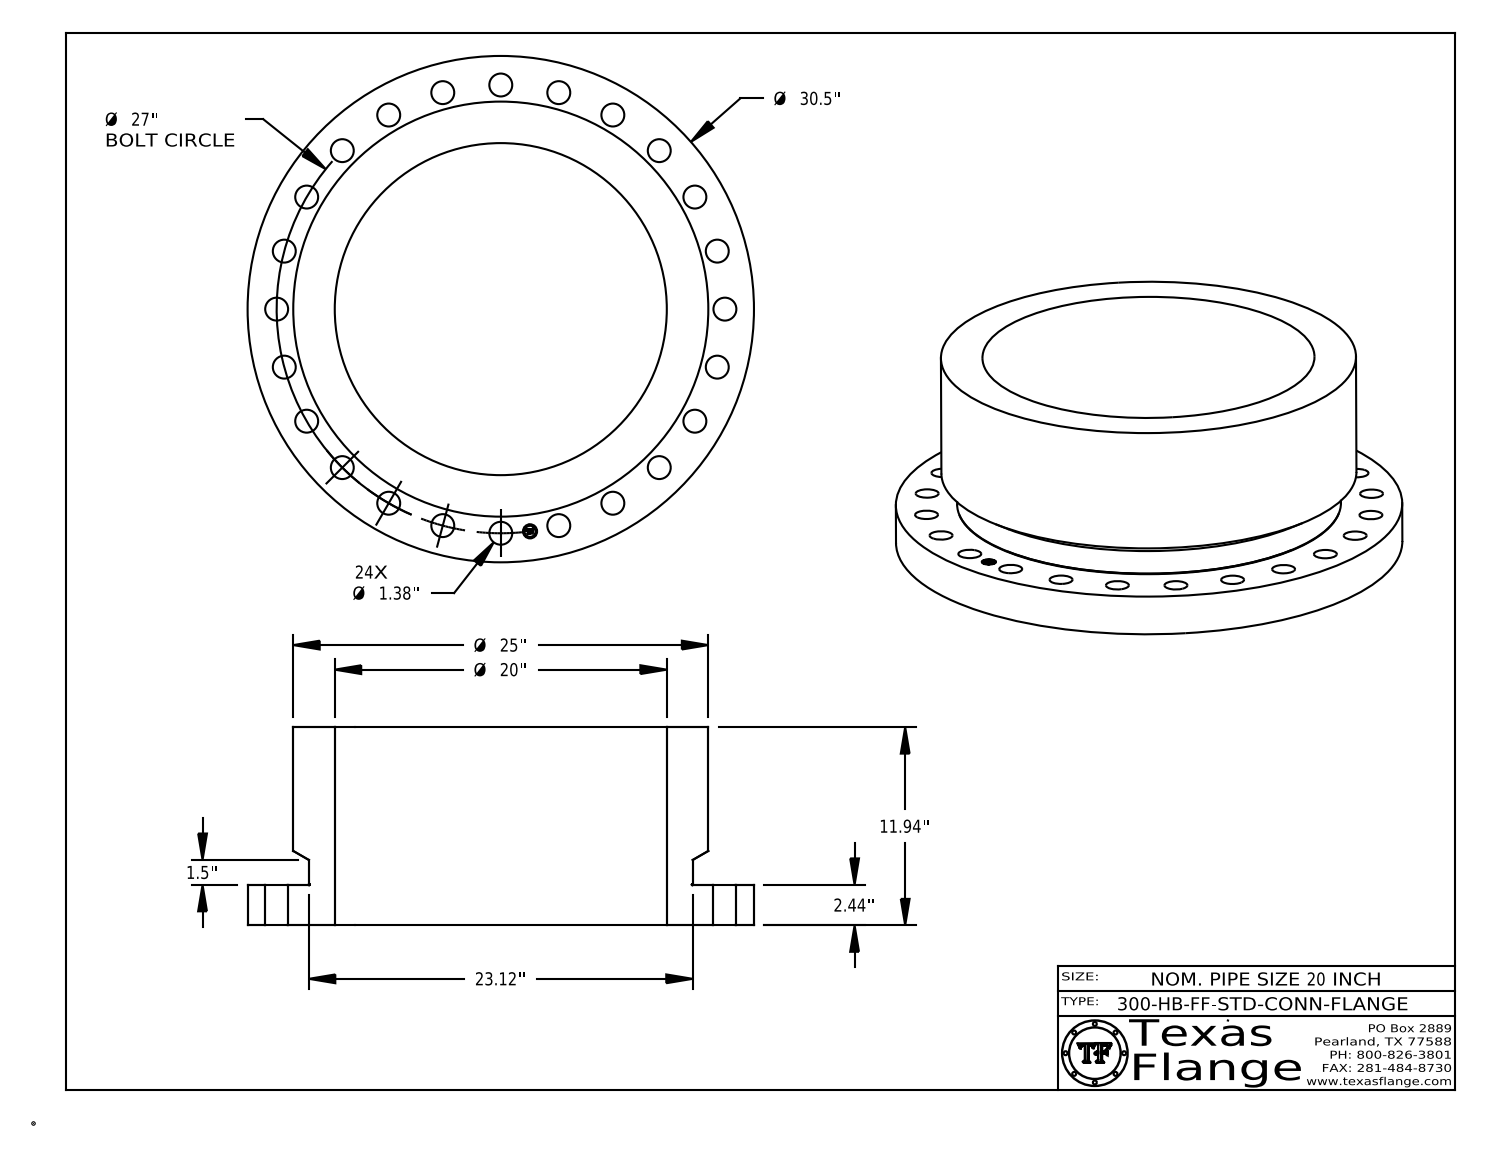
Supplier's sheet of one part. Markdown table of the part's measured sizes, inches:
| quantity | value |
| --- | --- |
| part name | 20-300-HB-FF-STD-CONN-FLANGE |
| STEP written by | CATIA V5 STEP AP214 (AUTOMOTIVE_DESIGN) |
| units | inches |
| bodies | 1 solid, 450 faces (368 planar, 76 cylindrical, 6 other) |
| overall size | 30.5 × 30.5 × 11.937 |
| volume | 2 480 in³ |
| surface area | 2 849 in² |
| round holes (diameter × count) | 1.38 × 24, 0.85 × 1, 20 × 1 |
| round bosses / shafts (diameter × count) | 0.051 × 8, 30.5 × 1, 25 × 1, 23.12 × 1, 0.67 × 1 |
| main face-to-face distances | 2.437, 11.937, 9.5, 2.433, 9.505, 0.254, 0.248, 0.016, 0.046, 0.165 |
| hole center spacings | 13.5, 3.524, 6.988, 10.333, 16.437, 24.945, 26.769, 21.421 |
